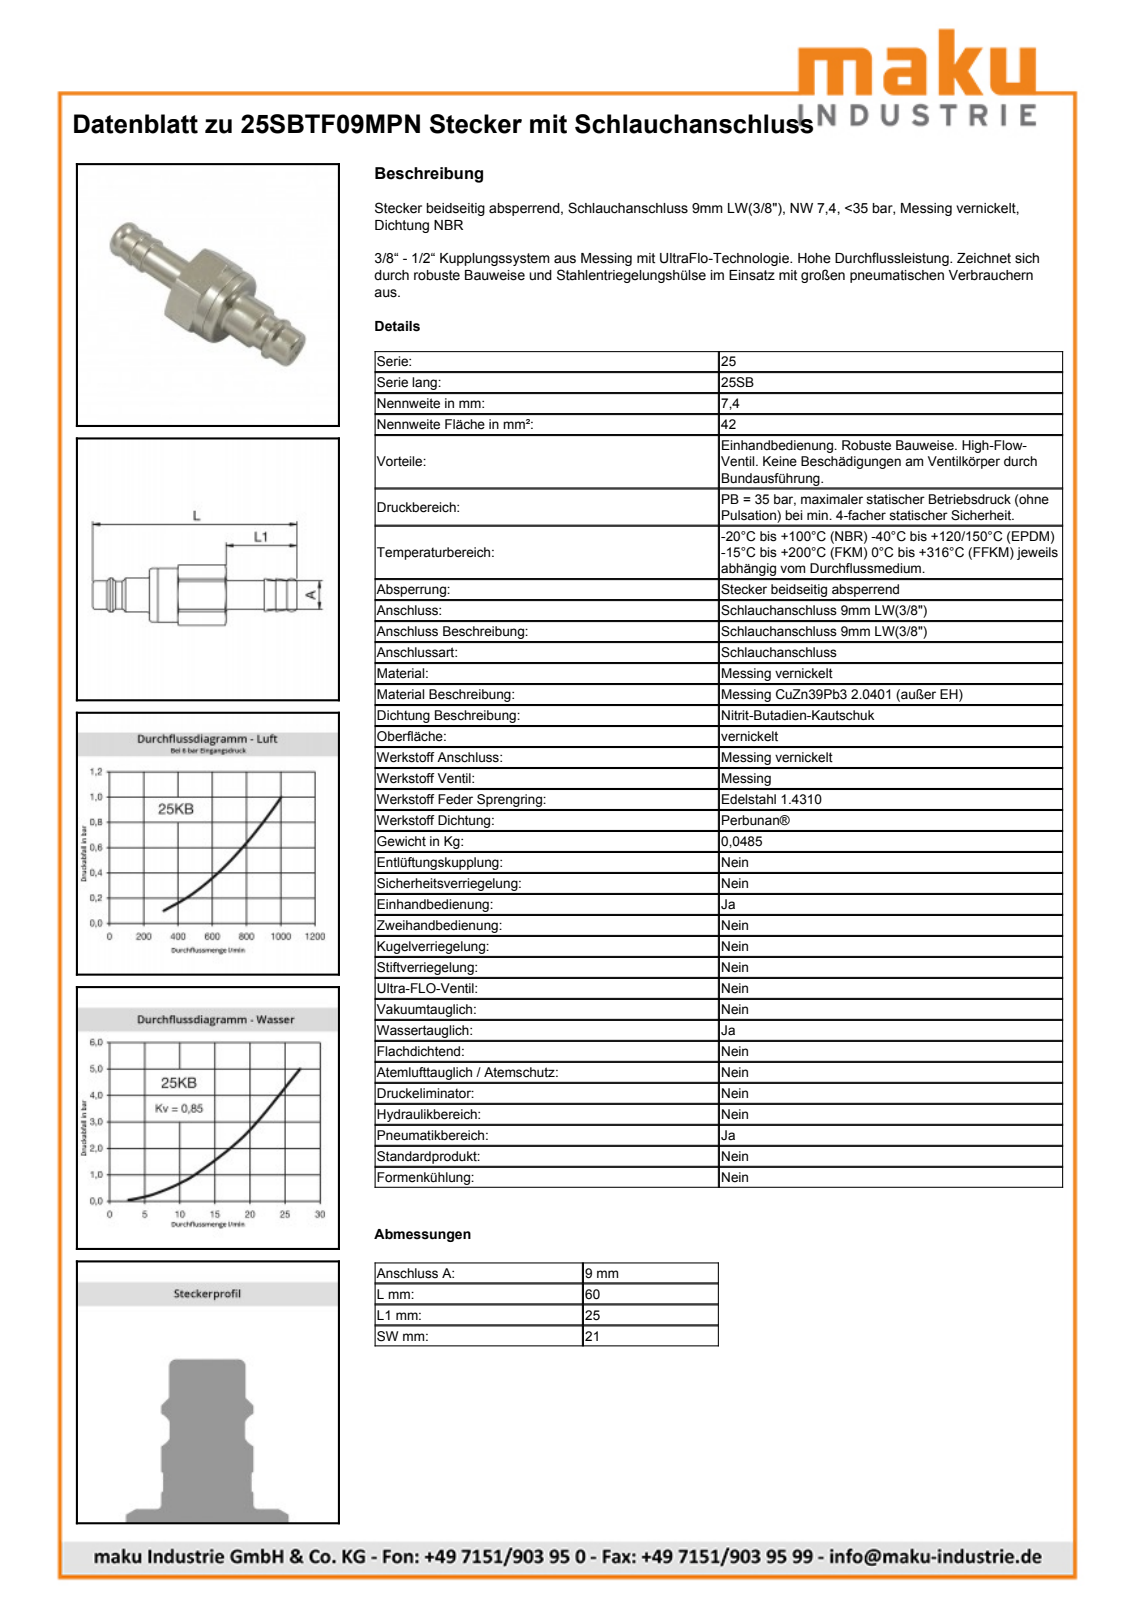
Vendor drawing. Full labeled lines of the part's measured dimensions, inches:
Part name (STEP PRODUCT): D106093
STEP written by: Autodesk Inventor 2011 (AUTOMOTIVE_DESIGN)
Units: inches
Bodies: 1 solid, 64 faces (18 planar, 19 cylindrical, 27 other)
Overall size (bounding box): 2.835 × 0.843 × 0.748
Volume: 0.712 in³ · Surface area: 6.969 in²
Round holes (diameter × count): ⌀0.309 ×1, ⌀0.594 ×1, ⌀0.63 ×1
Round bosses / shafts (diameter × count): ⌀0.748 ×1, ⌀0.746 ×1, ⌀0.738 ×1, ⌀0.472 ×1, ⌀0.39 ×1, ⌀0.384 ×1, ⌀0.358 ×1
Partial cylindrical surfaces — rounded edges, fillets, slot ends (radius × count): R0.421 ×1
Main face-to-face distances: 0.748, 1.063, 1.85, 0.984, 0.787, 2.835, 2.047, 0.295, 1.752, 0.118
